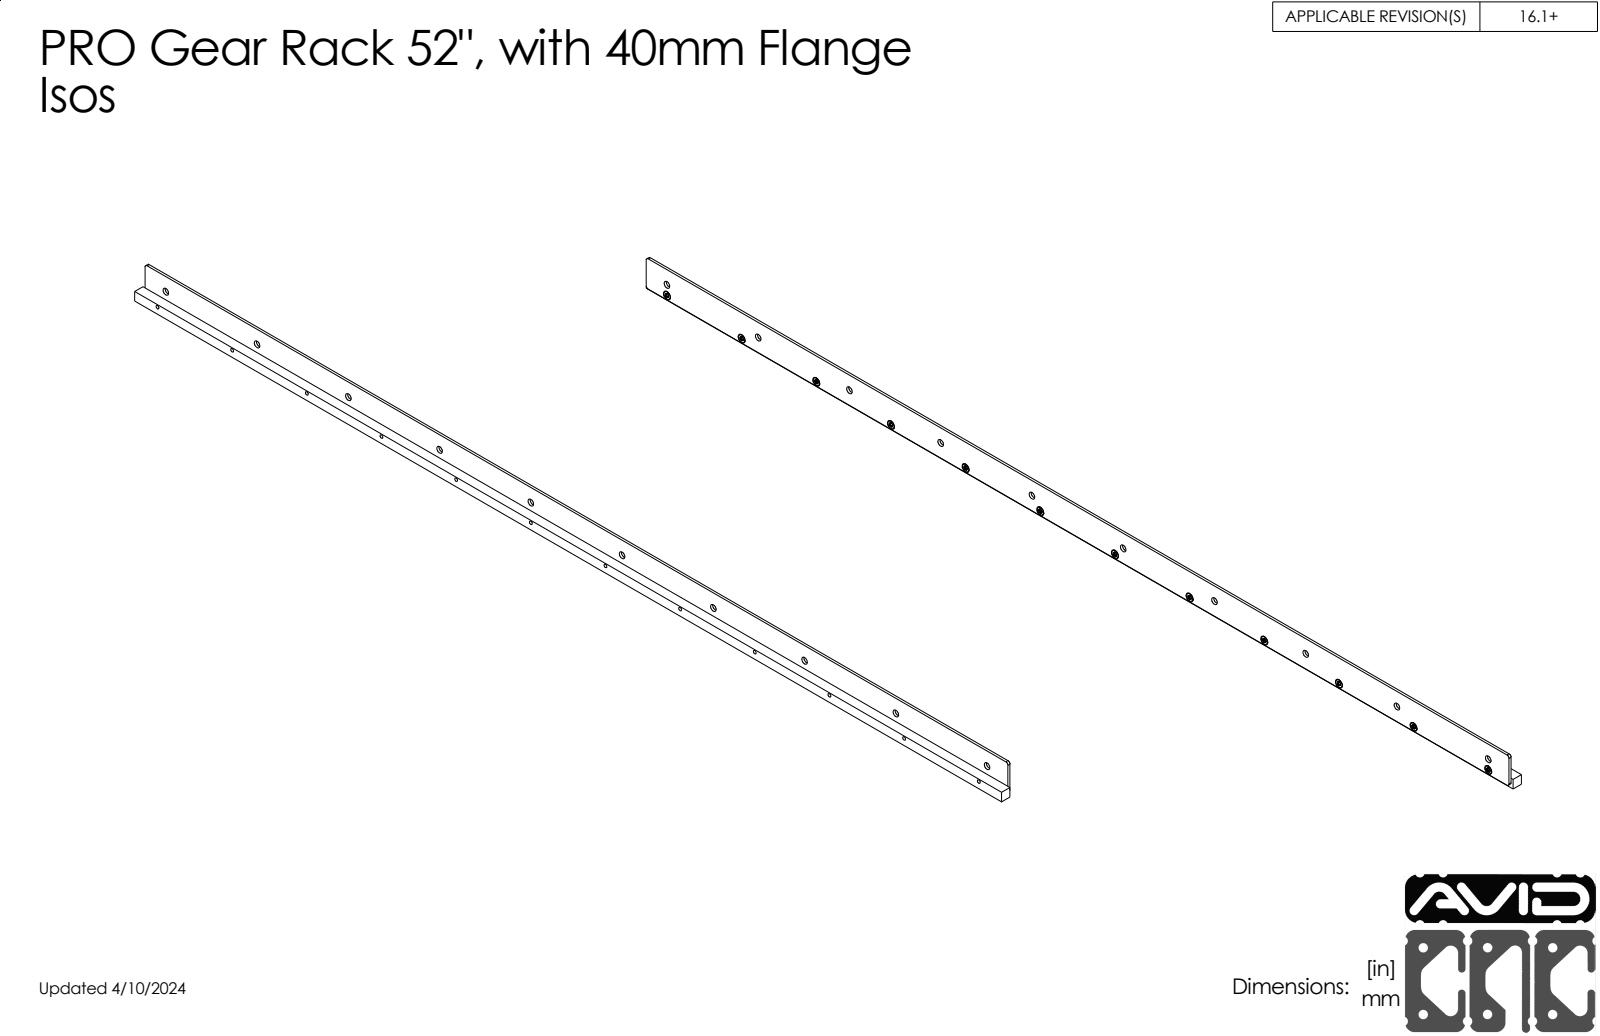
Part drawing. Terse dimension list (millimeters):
name: MG-XX-ME-PRO_52"; Flathead Machine Screws, Torx Drive - Metric_FH-M5-10-TX; MGM-52-40_16.1; MGM-XX-BAR-40_52" Bar
written by: SolidWorks 2020 (CONFIG_CONTROL_DESIGN)
unit: mm
bodies: 14 solids, 480 faces (36 planar, 120 cylindrical, 324 other)
size: 1327.15 × 43.56 × 15.88
volume: 379 202 mm³; area: 186 792 mm²
holes: 12× ⌀4.2, 12× ⌀5.5, 10× ⌀8.38
bosses: 12× ⌀9.3, 12× ⌀5
rounds: 4× R3.17
face distances: 3.17, 12.7, 15.87, 3.56, 43.56, 9.14, 40, 30.86, 3.07, 15.77
hole spacings: 114.3, 228.6, 139.7, 342.9, 279.4, 457.2, 419.1, 571.5
